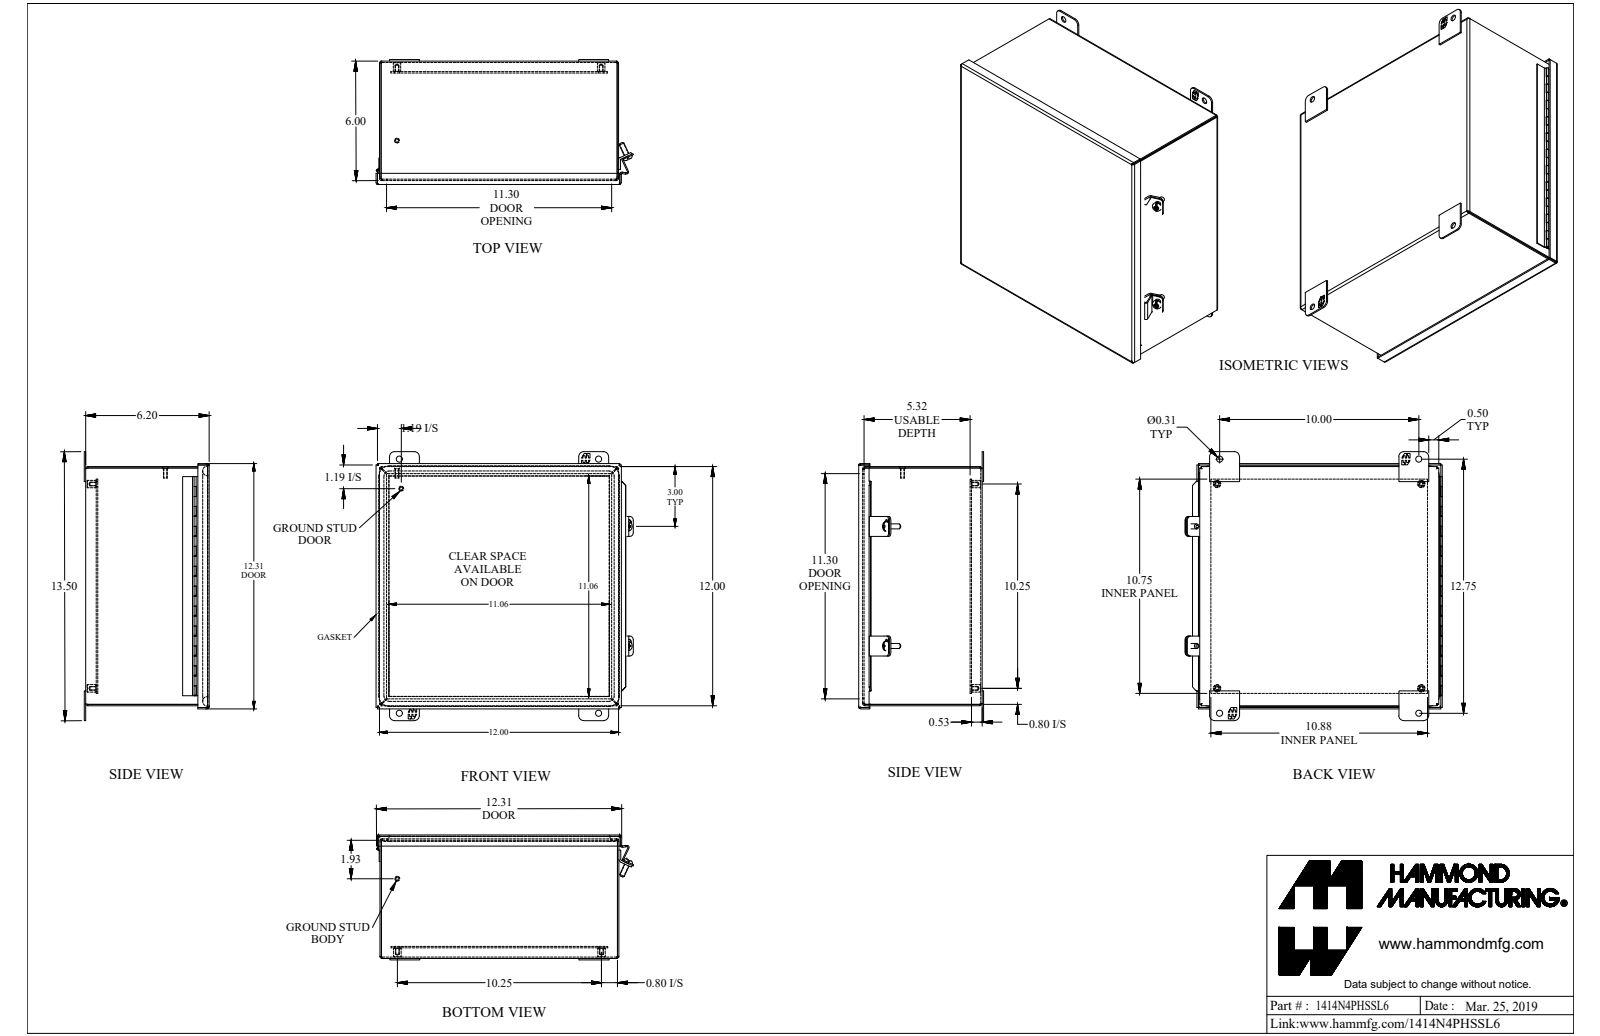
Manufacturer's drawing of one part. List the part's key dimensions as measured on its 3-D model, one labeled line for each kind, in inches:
Part name (STEP PRODUCT): 1414N4PHSSL6
STEP written by: SolidWorks 2018 (AUTOMOTIVE_DESIGN)
Units: inches
Bodies: 21 solids, 716 faces (456 planar, 196 cylindrical, 64 other)
Overall size (bounding box): 13.5 × 12.903 × 6.269
Volume: 58.75 in³ · Surface area: 1 647 in²
Round holes (diameter × count): ⌀0.156 ×4, ⌀0.265 ×4, ⌀0.313 ×4, ⌀0.213 ×2, ⌀0.05 ×1
Round bosses / shafts (diameter × count): ⌀0.375 ×4, ⌀0.25 ×4, ⌀0.48 ×2, ⌀0.19 ×2, ⌀0.1 ×1, ⌀0.045 ×1
Partial cylindrical surfaces — rounded edges, fillets, slot ends (radius × count): R0.25 ×24, R0.036 ×8, R0.108 ×8, R0.188 ×8, R0.007 ×4, R0.046 ×4, R0.079 ×4, R0.118 ×4
Main face-to-face distances: 0.072, 6.125, 11.928, 5.593, 0.532, 6.197, 6.053, 11.856, 12, 0.604
Hole centre spacings: 10.25, 10.25, 10.202, 1.256, 11.501, 14.496, 15.322, 1.256
